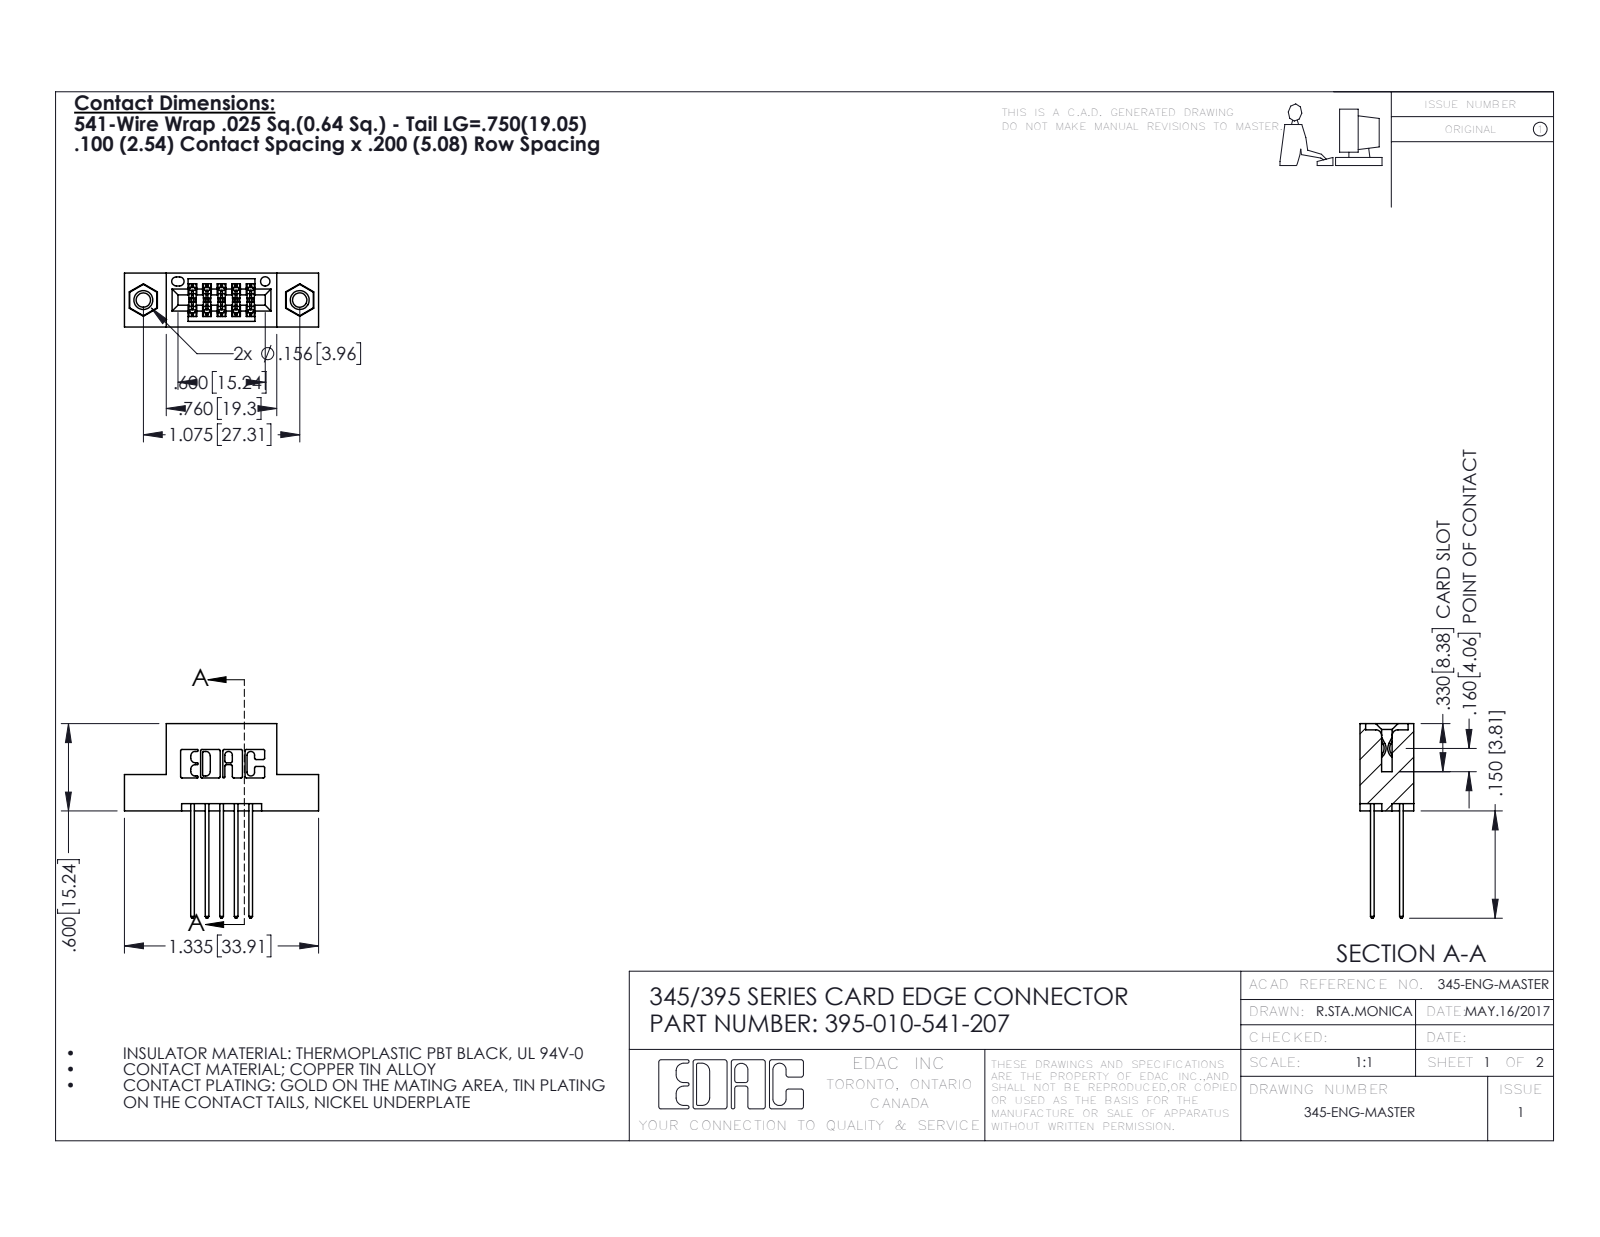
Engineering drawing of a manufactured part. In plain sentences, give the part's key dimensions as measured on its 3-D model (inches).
The part is named "345-250-001_345-250-005-103; 345-292-001_345-293-141; 395-010-541-207; 345 Part_Flush Mounting Lugs - 0.156 Dia-TI". Its 3-D file was written by "SolidWorks 2016 (CONFIG_CONTROL_DESIGN)". It is 13 solids with 686 faces: 442 planar, 228 cylindrical and 16 other. Overall it measures 1.337 by 1.335 by 0.37 inches. Its volume is 0.183 cubic inches and its surface area 6.211 square inches. Round holes: 2 of diameter 0.098, 2 of diameter 0.125, 2 of diameter 0.156, 1 of diameter 0.064. Round bosses or shafts: 2 of diameter 0.155. Partial cylindrical surfaces (rounded edges, fillets, slot ends): 22 of radius 0.01, 15 of radius 0.006, 10 of radius 0.01, 6 of radius 0.007, 6 of radius 0.031, 3 of radius 0.026, 2 of radius 0.014, 2 of radius 0.019. The main face-to-face distances are 0.2, 0.072, 0.298, 0.1, 0.37, 0.098, 0.272, 0.025, 0.225, 0.35. The hole center spacings are 0.27, 0.847, 1.075.
